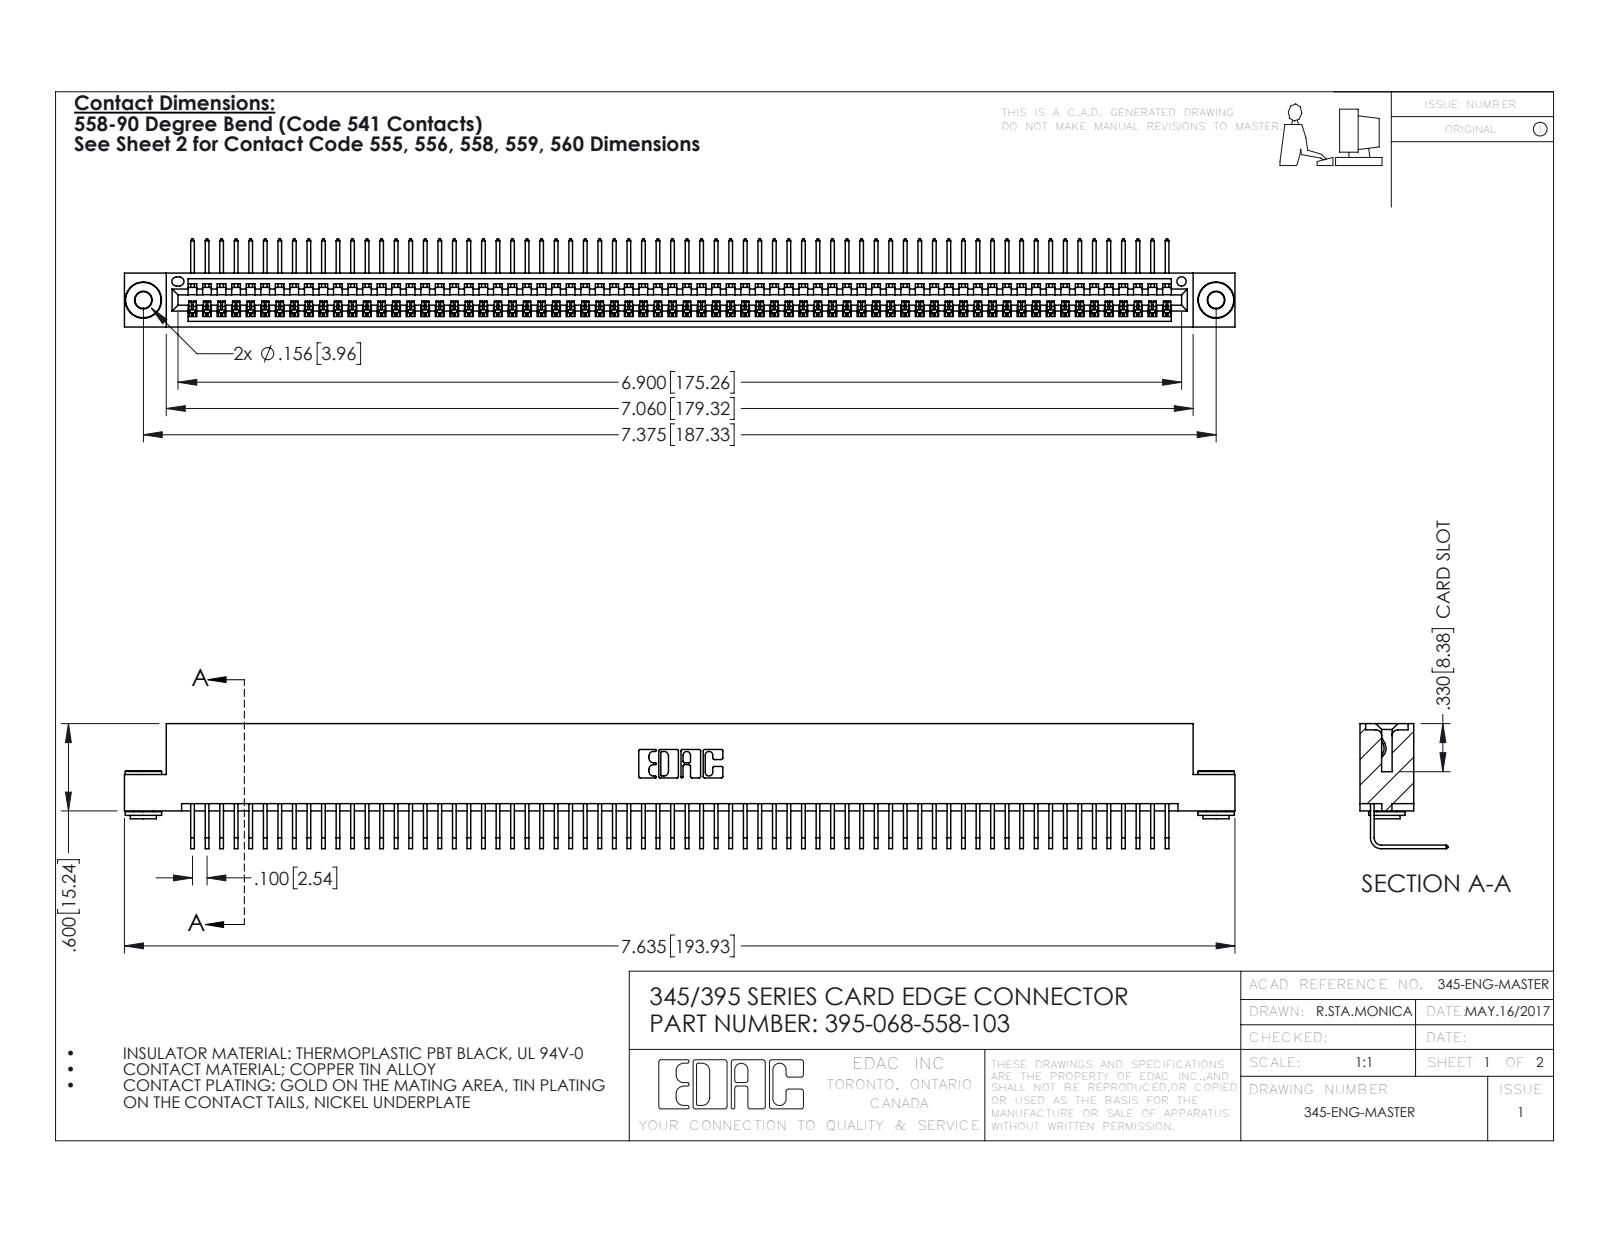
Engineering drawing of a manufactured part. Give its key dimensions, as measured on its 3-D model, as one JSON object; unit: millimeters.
{"part_name": "395-068-558-103; 345 Part_Flush Mounting Lugs - 0.156 Dia-TH; 345-250-002_345-250-002-102; 345-292-001_558 Tail - 2", "step_written_by": "SolidWorks 2016 (CONFIG_CONTROL_DESIGN)", "units": "millimeters", "bodies": {"solids": 71, "faces": 4244, "planar": 2946, "cylindrical": 1290, "other": 8}, "overall_size": [193.9, 21.8, 15.4], "volume_mm3": 18880, "surface_area_mm2": 26990, "round_holes": [[2.9, 2], [4, 2], [1.6, 1]], "round_bosses_or_shafts": [[6.4, 2], [4.6, 2], [3.5, 2]], "partial_cylinders_radius": [[0.2, 136], [0.3, 22], [0.2, 6], [0.8, 6], [0.7, 3], [0.8, 2], [1, 2], [0.4, 1]], "face_to_face_distances": [1.8, 7.6, 9.4, 5.1, 0.6, 2.5, 6.9, 5.7, 3.8, 1.8], "hole_center_spacings": [6.9, 181.3, 187.3]}
